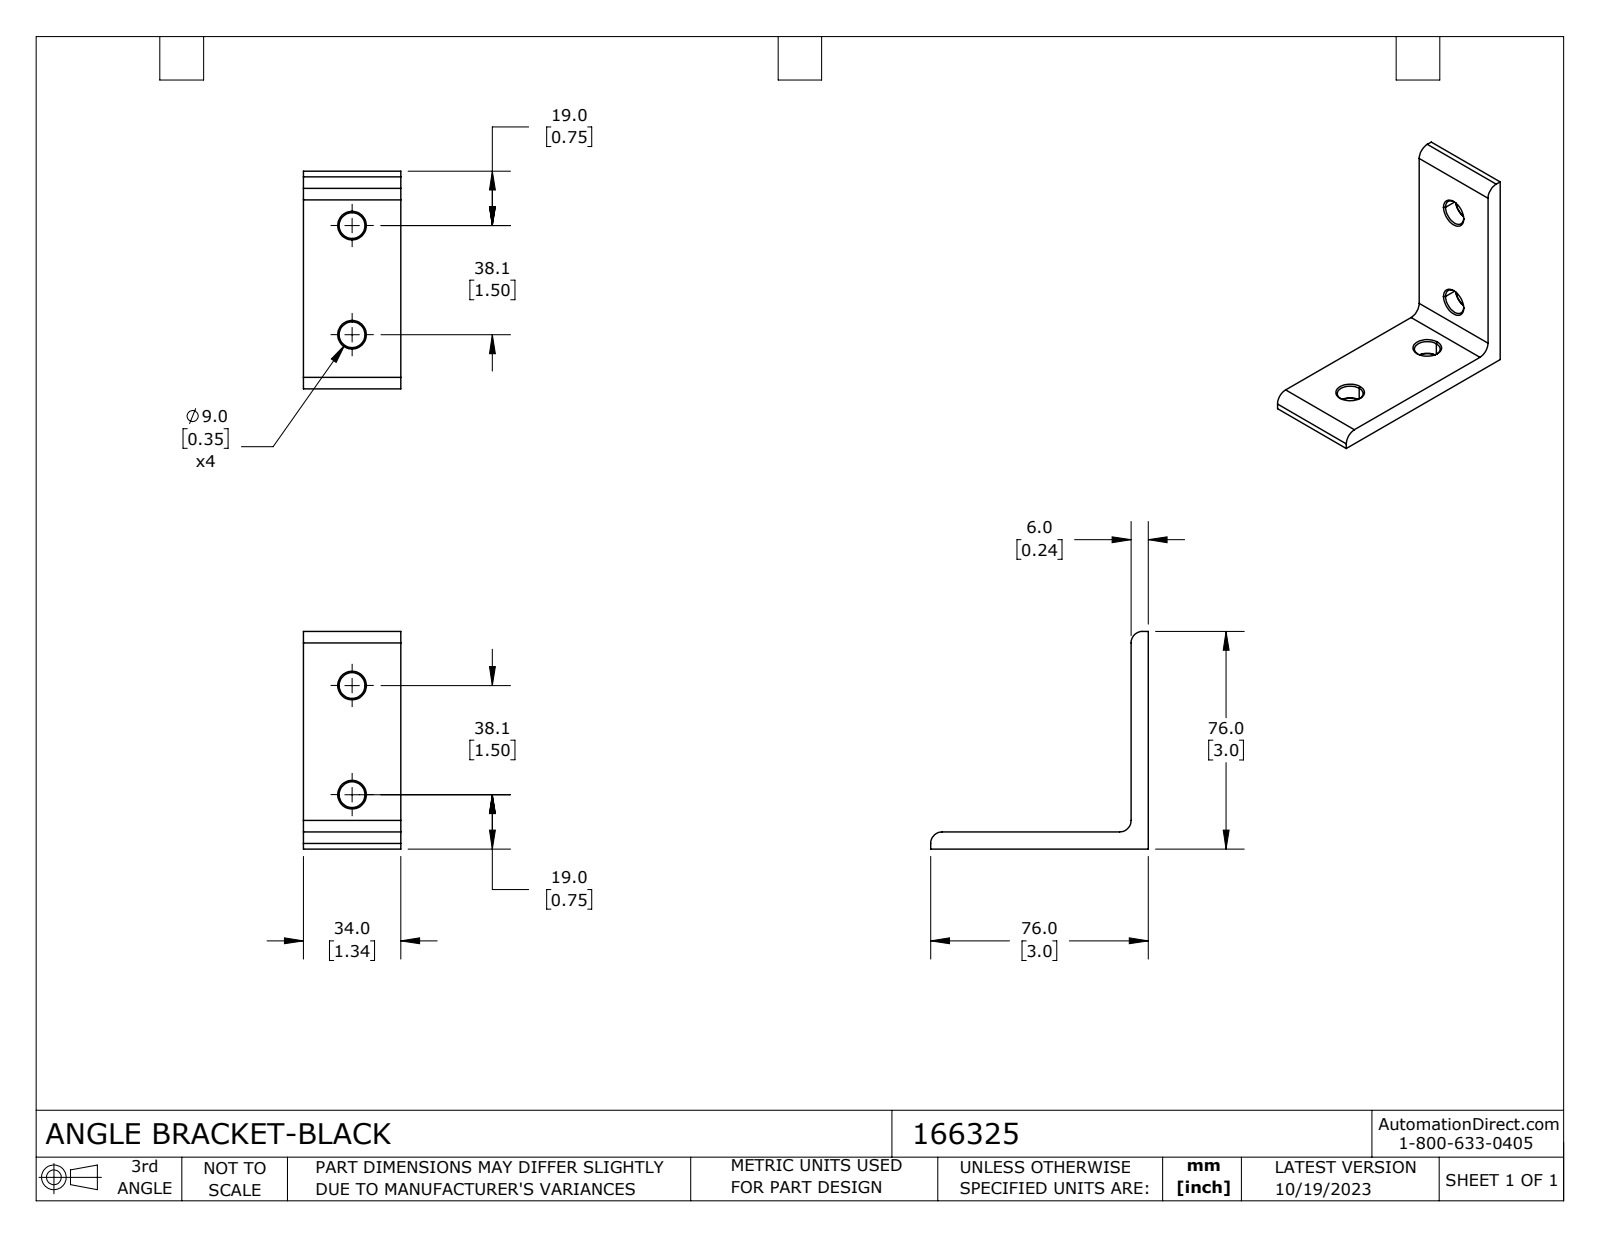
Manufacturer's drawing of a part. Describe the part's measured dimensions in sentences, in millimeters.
The part is named "166325". Its 3-D file was written by "SolidWorks 2023 (CONFIG_CONTROL_DESIGN)". It is 1 solid with 35 faces: 8 planar, 11 cylindrical and 16 other. Overall it measures 76 by 76 by 34 millimeters. Its volume is 28 111 cubic millimeters and its surface area 12 012 square millimeters. Round holes: 4 of diameter 9. Partial cylindrical surfaces (rounded edges, fillets, slot ends): 3 of radius 4. The main face-to-face distances are 6, 34, 76, 70. The hole center spacings are 38.1.
